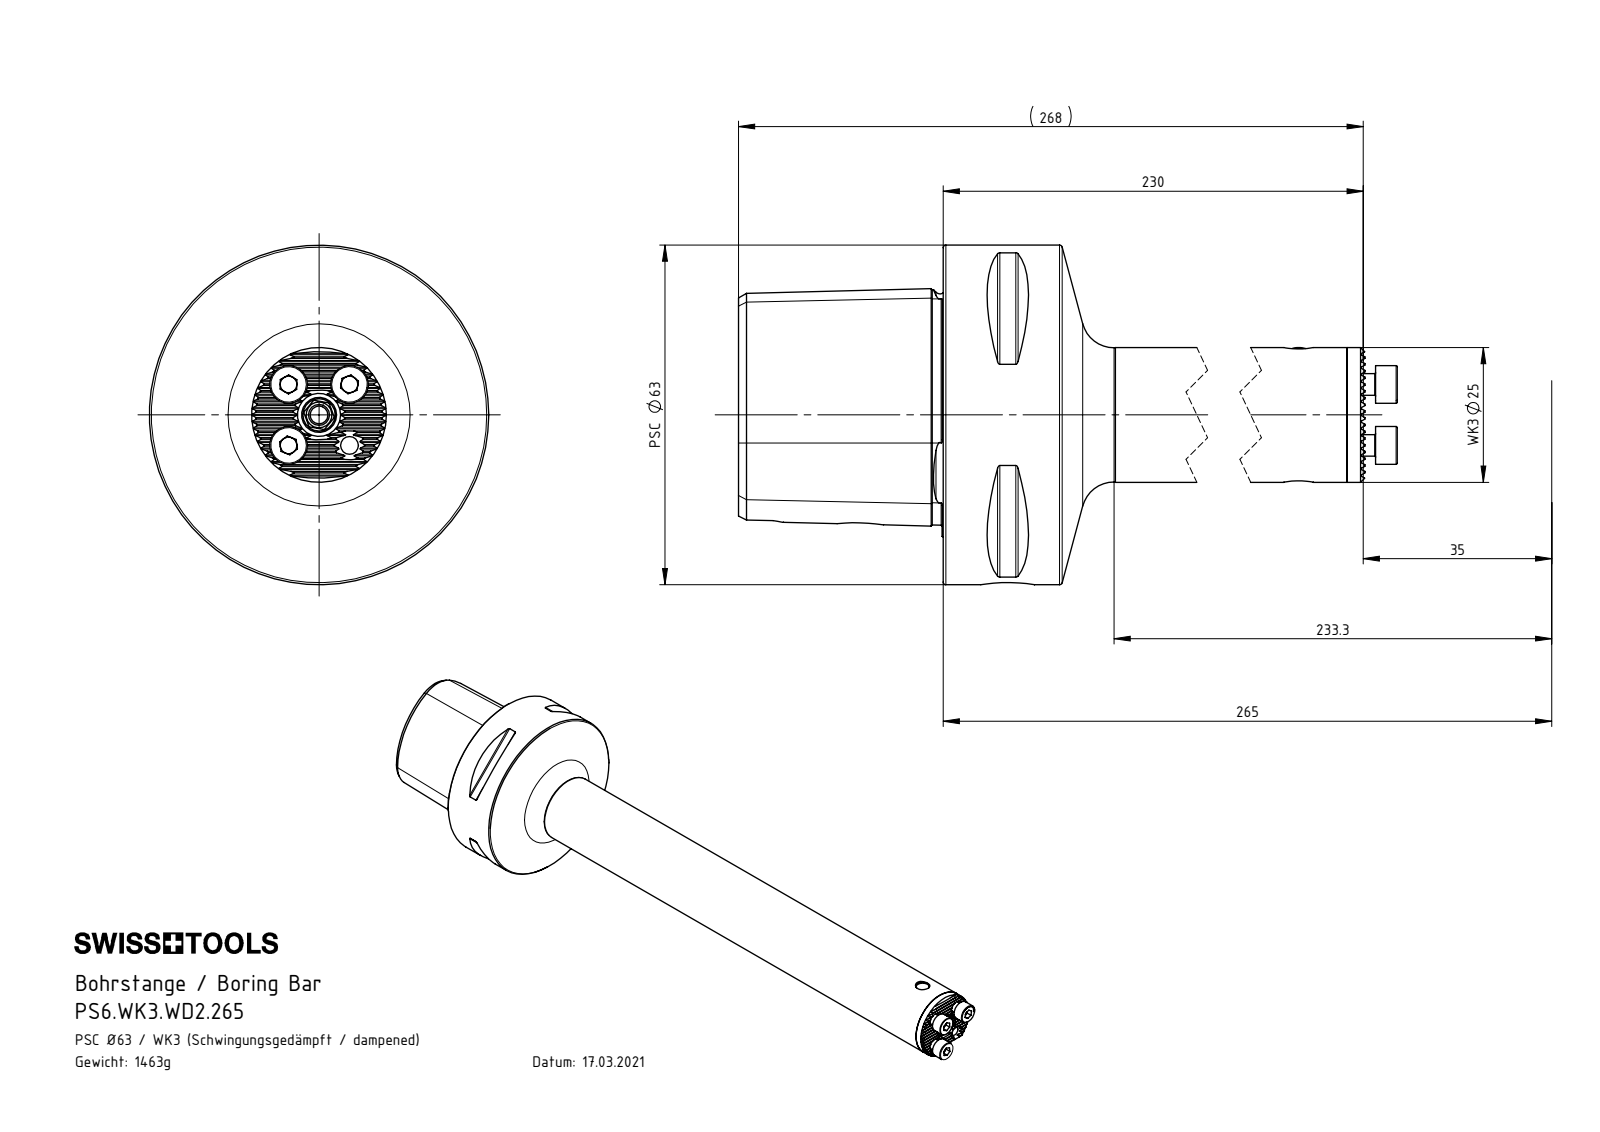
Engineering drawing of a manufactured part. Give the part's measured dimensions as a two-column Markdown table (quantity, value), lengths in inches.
| quantity | value |
| --- | --- |
| part name | ISO 4762 - M4 x 12; WD2-BG1.021.085; DIN 3771 - 17x2; DIN 3771 - 10x4 (+8 more) |
| STEP written by | SolidWorks 2017 (AUTOMOTIVE_DESIGN) |
| units | inches |
| bodies | 16 solids, 493 faces (237 planar, 110 cylindrical, 146 other) |
| overall size | 10.799 × 2.48 × 2.48 |
| volume | 11.55 in³ |
| surface area | 101.7 in² |
| round holes (diameter × count) | 0.13 × 5, 0.197 × 1, 0.217 × 1, 0.236 × 1, 0.256 × 1, 0.268 × 1, 0.291 × 1, 0.319 × 1, 0.354 × 1, 0.394 × 1, 0.402 × 1, 0.433 × 1 |
| round bosses / shafts (diameter × count) | 0.276 × 3, 0.157 × 3, 2.48 × 1, 0.984 × 1, 0.827 × 1, 0.815 × 1, 0.787 × 1, 0.701 × 1 |
| partial cylindrical surfaces (radius × count) | 0.005 × 19, 0.02 × 8, 0.236 × 1 |
| main face-to-face distances | 0.236, 1.496, 3.087, 0.126, 0.98, 0.17, 9.803, 8.307, 0.043, 0.362 |
| hole center spacings | 0.315, 0.446, 0.63, 1.083, 8.11, 9.193 |
